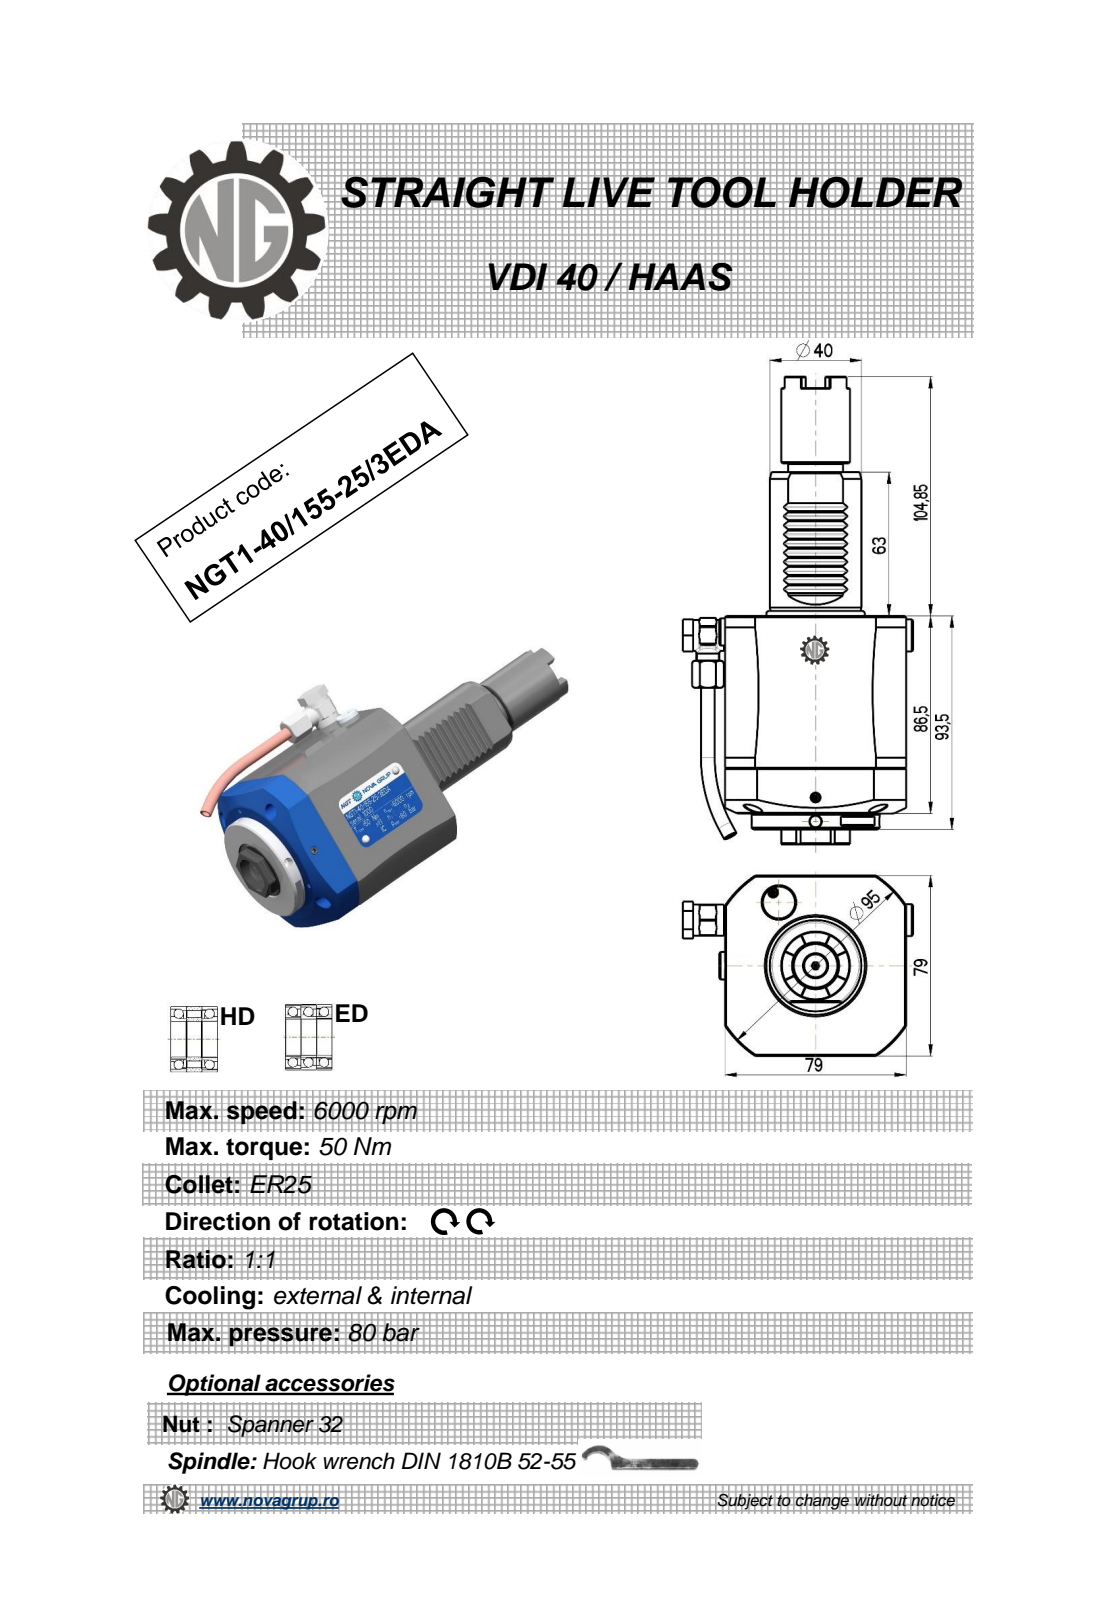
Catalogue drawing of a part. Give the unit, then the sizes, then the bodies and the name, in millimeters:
Units: millimetres
Overall size (bounding box): 204.85 × 100.4 × 79
Round holes (diameter × count): ⌀4 ×3, ⌀5 ×2, ⌀3 ×1, ⌀6 ×1, ⌀6.2 ×1, ⌀9 ×1, ⌀10 ×1, ⌀11 ×1, ⌀18 ×1, ⌀26.5 ×1
Round bosses / shafts (diameter × count): ⌀56 ×1, ⌀40 ×1, ⌀30 ×1, ⌀24 ×1, ⌀14 ×1, ⌀13.6 ×1, ⌀13 ×1, ⌀12 ×1
Partial cylindrical surfaces — rounded edges, fillets, slot ends (radius × count): R0.3 ×10, R0.41 ×6, R0.5 ×4, R7.7 ×1, R10 ×1, R47 ×1, R47.5 ×1
Main face-to-face distances: 79, 86.5, 7, 93.5, 2.83, 156.5, 149.5, 63, 8.48, 14.14
Hole centre spacings: 0.4, 51.08, 51.45, 83.92
Volume: 627 153 mm³ · Surface area: 57 303 mm²
Bodies: 2 solids, 420 faces (180 planar, 111 cylindrical, 129 other)
Part name (STEP PRODUCT): NGT1_40_155_25_3HDA
STEP written by: PRO/ENGINEER BY PARAMETRIC TECHNOLOGY CORPORATION, 2010280 (CONFIG_CONTROL_DESIGN)
